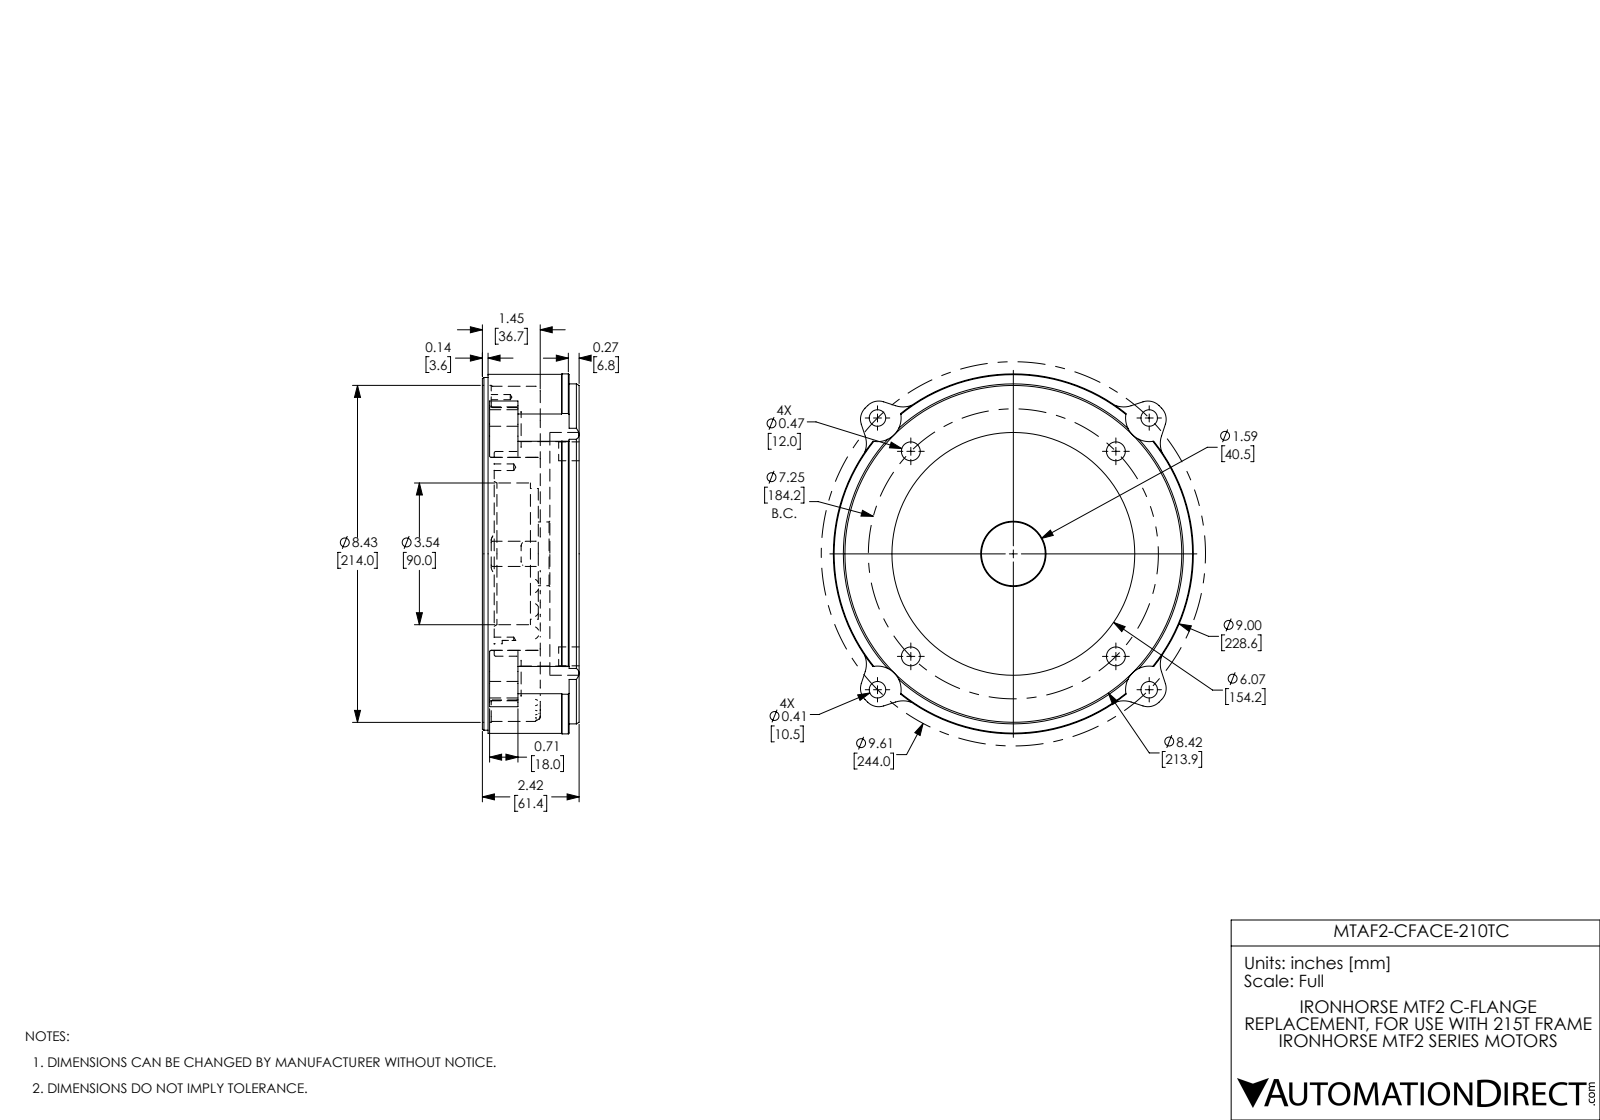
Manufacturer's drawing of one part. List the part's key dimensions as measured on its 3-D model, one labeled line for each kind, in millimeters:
Part name (STEP PRODUCT): MTAF2-CFACE-210TC coord norm
STEP written by: SolidWorks 2017 (AUTOMOTIVE_DESIGN)
Units: millimetres
Bodies: 1 solid, 402 faces (56 planar, 163 cylindrical, 183 other)
Overall size (bounding box): 228.6 × 228.6 × 61.4
Volume: 1 006 000 mm³ · Surface area: 187 600 mm²
Round holes (diameter × count): ⌀10.5 ×4, ⌀12 ×4, ⌀4.2 ×2, ⌀3.3 ×1, ⌀40.5 ×1, ⌀83 ×1, ⌀90 ×1, ⌀154.2 ×1, ⌀214 ×1
Round bosses / shafts (diameter × count): ⌀228.6 ×1, ⌀228 ×1, ⌀224 ×1, ⌀215.9 ×1, ⌀110 ×1
Partial cylindrical surfaces — rounded edges, fillets, slot ends (radius × count): R3 ×36, R1 ×14, R15 ×12, R10 ×8, R25 ×4, R65 ×1, R93 ×1, R132 ×1
Main face-to-face distances: 6.1, 24.7, 18.6, 1.2, 7.3, 25.9, 19.6, 18.3, 12.3, 6.4
Hole centre spacings: 152.9, 29.9, 65.9, 91.8, 92.1, 122, 130.2, 136.6
